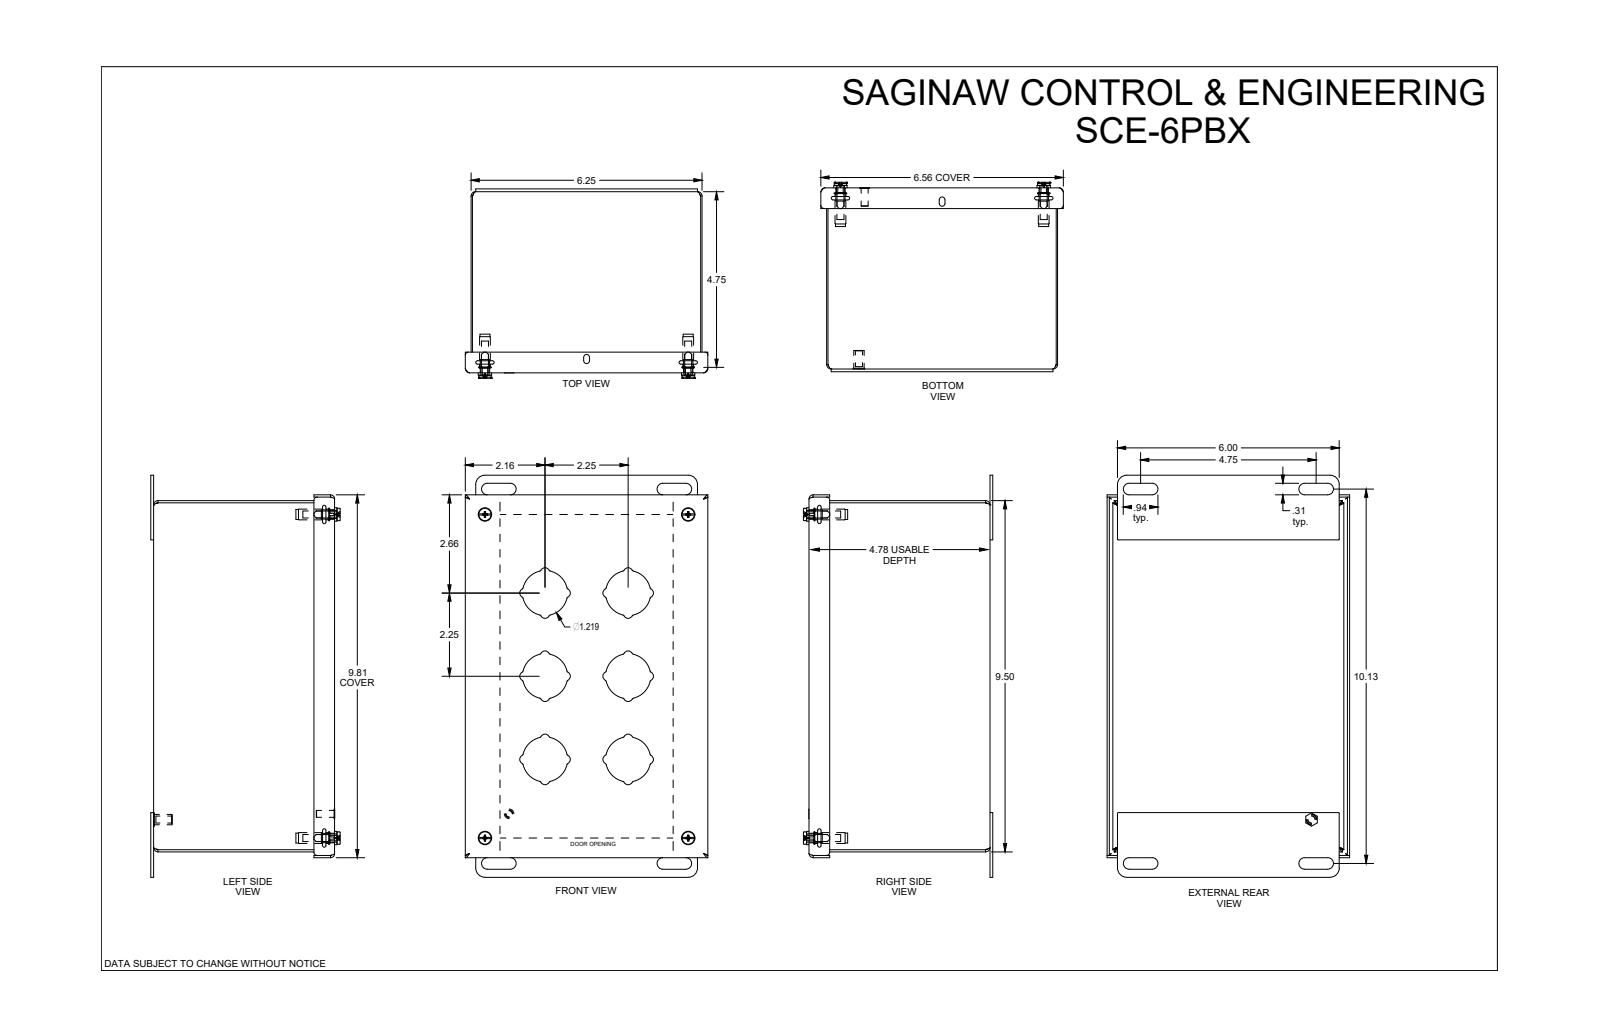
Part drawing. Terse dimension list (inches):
name: SCE-6PBX
written by: SolidWorks 2019 (CONFIG_CONTROL_DESIGN)
unit: in
bodies: 0 solids, 674 faces (266 planar, 246 cylindrical, 162 other)
size: 10.875 × 6.563 × 5.124
holes: 5× ⌀0.19, 4× ⌀0.22, 4× ⌀0.25, 4× ⌀0.317, 1× ⌀0.281
bosses: 5× ⌀0.188, 4× ⌀0.362, 4× ⌀0.34, 4× ⌀0.334, 4× ⌀0.292, 4× ⌀0.27, 4× ⌀0.266, 4× ⌀0.26
rounds: 48× R0.04, 24× R0.125, 8× R0.015, 8× R0.052, 8× R0.112, 8× R0.115, 8× R0.156, 8× R0.245
face distances: 0.06, 4.838, 6.19, 9.44, 4.778, 4.898, 6.13, 6.25, 4.69, 0.148
hole spacings: 5.5, 8.75, 10.335, 0.707, 5.025, 8.265, 9.647
